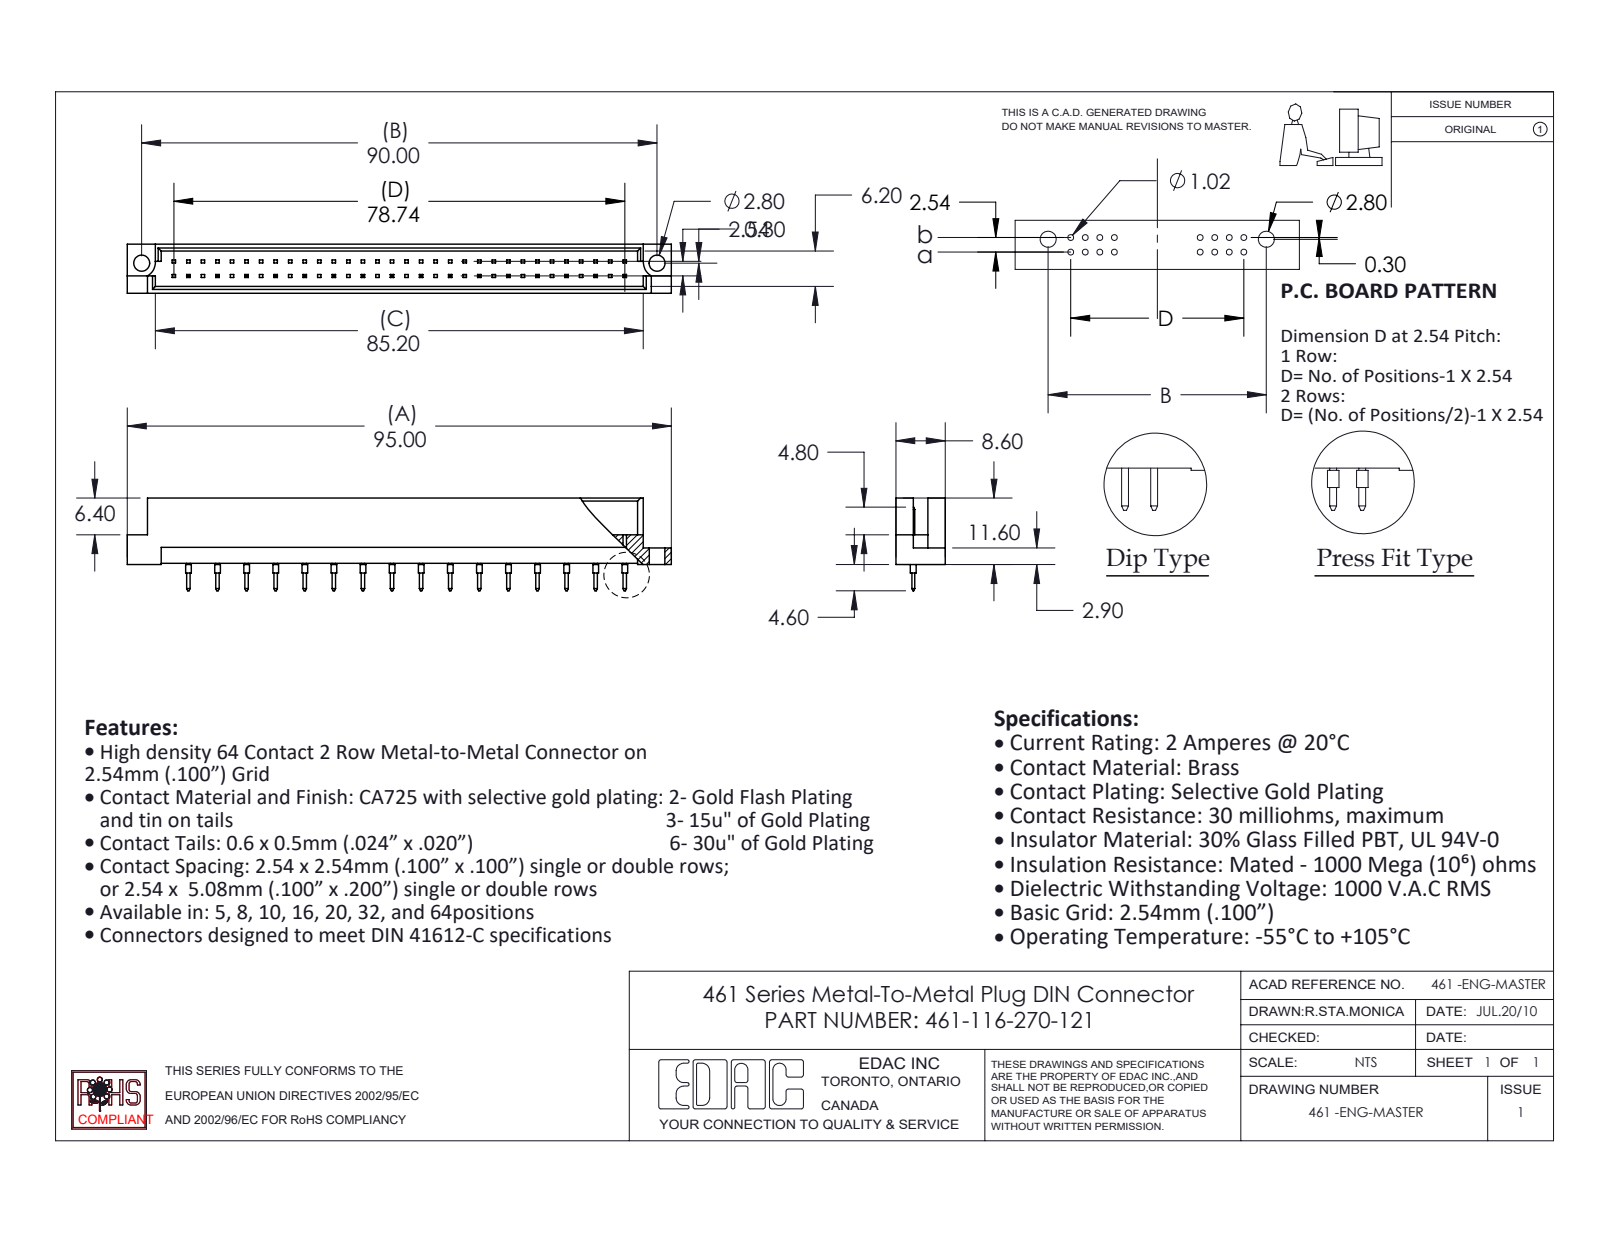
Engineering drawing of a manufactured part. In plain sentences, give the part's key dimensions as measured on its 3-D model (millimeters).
The part is named "461 Part_64; 461-116-270-221; 461-290_70". Its 3-D file was written by "SolidWorks 2020 (CONFIG_CONTROL_DESIGN)". It is 17 solids with 657 faces: 618 planar, 39 cylindrical and 0 other. Overall it measures 95 by 16.2 by 8.6 millimeters. Its volume is 4 737 cubic millimeters and its surface area 6 218 square millimeters. Round holes: 2 of diameter 2.8. Round bosses or shafts: 16 of diameter 1. Partial cylindrical surfaces (rounded edges, fillets, slot ends): 2 of radius 2.8. The main face-to-face distances are 1.2, 7.4, 8.6, 6.2, 5, 1.58, 3.28, 5.32, 2.08, 4.12. The hole center spacings are 90.
